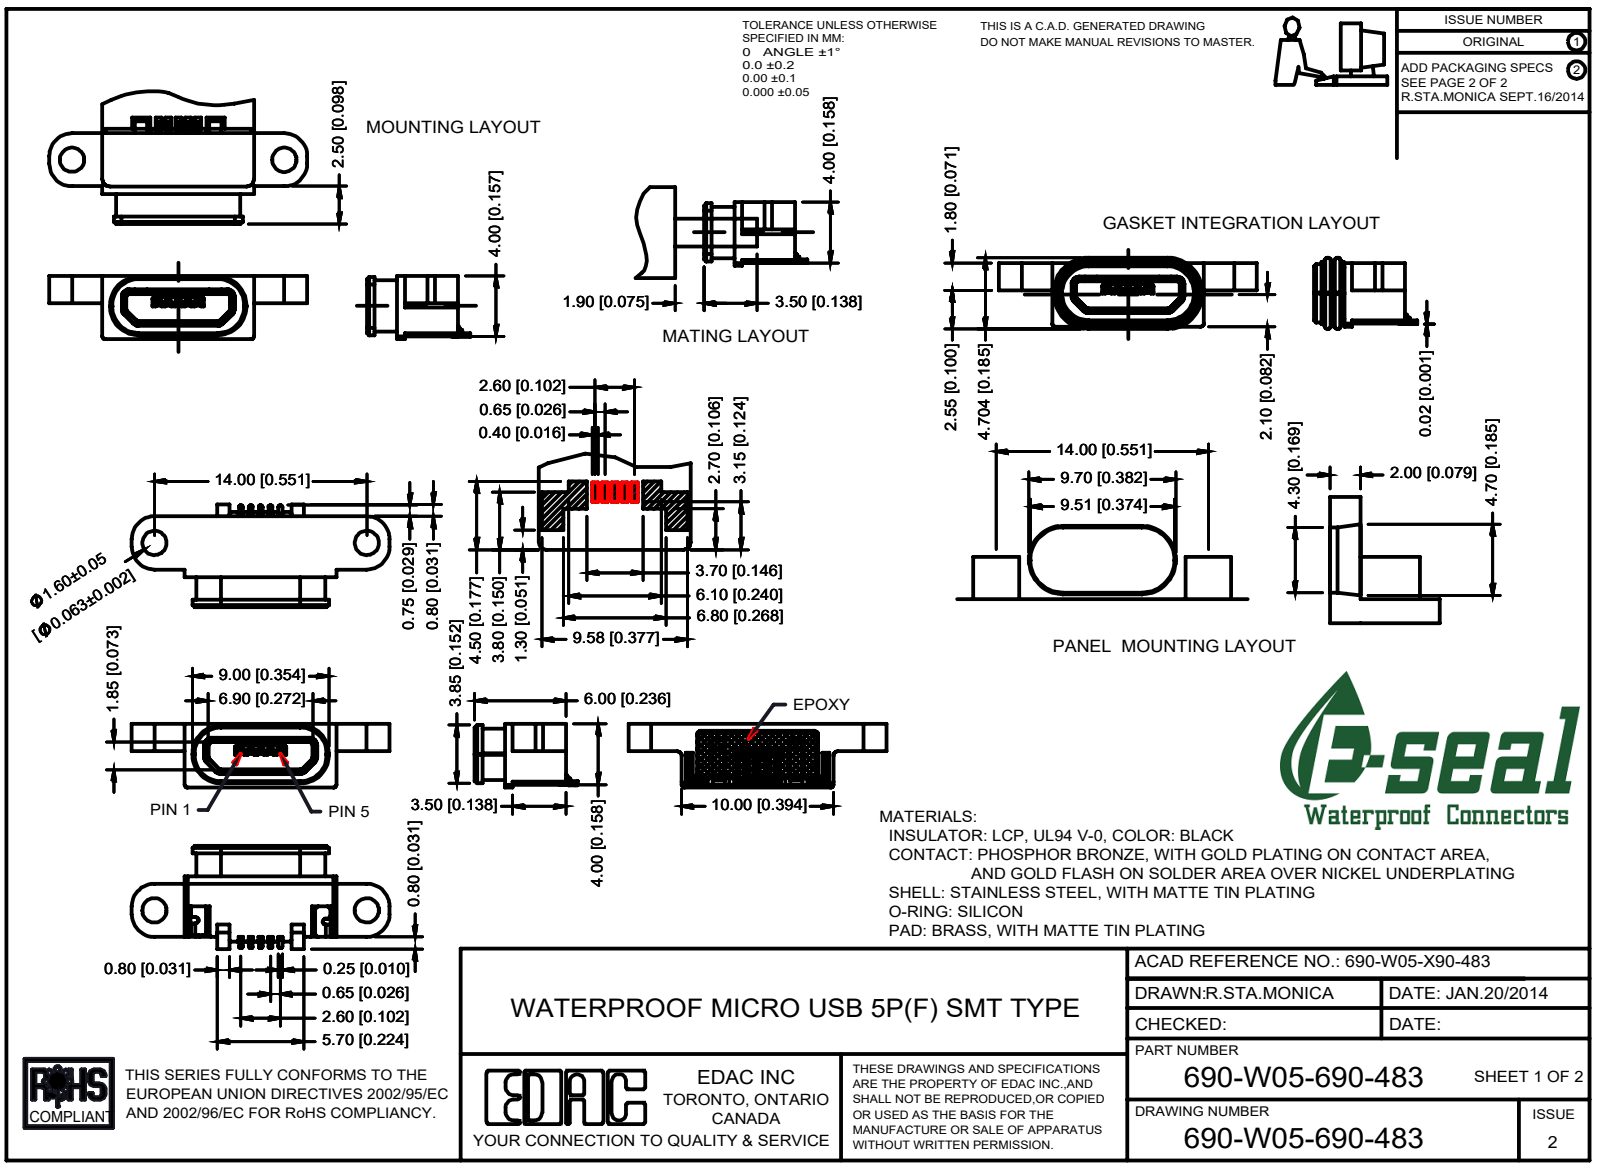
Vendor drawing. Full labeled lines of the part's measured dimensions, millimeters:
Part name (STEP PRODUCT): SHELL 690-W05-X90-483; SOLDER PADS 690-W05-X90-483; 690-W05-290-483; O-RING 690-W05-X90-483 (+2 more)
STEP written by: SolidWorks 2020 (AUTOMOTIVE_DESIGN)
Units: millimetres
Bodies: 10 solids, 637 faces (452 planar, 177 cylindrical, 8 other)
Overall size (bounding box): 17 × 6.8 × 5.7
Volume: 214 mm³ · Surface area: 828 mm²
Round holes (diameter × count): ⌀1.6 ×2
Partial cylindrical surfaces — rounded edges, fillets, slot ends (radius × count): R0.15 ×28, R0.2 ×20, R0.1 ×17, R0.5 ×16, R0.25 ×11, R0.3 ×8, R0.8 ×4, R1.5 ×4
Main face-to-face distances: 0.9, 2.1, 4, 1.5, 2.37, 2.13, 0.7, 0.6, 0.87, 0.93
Hole centre spacings: 14
